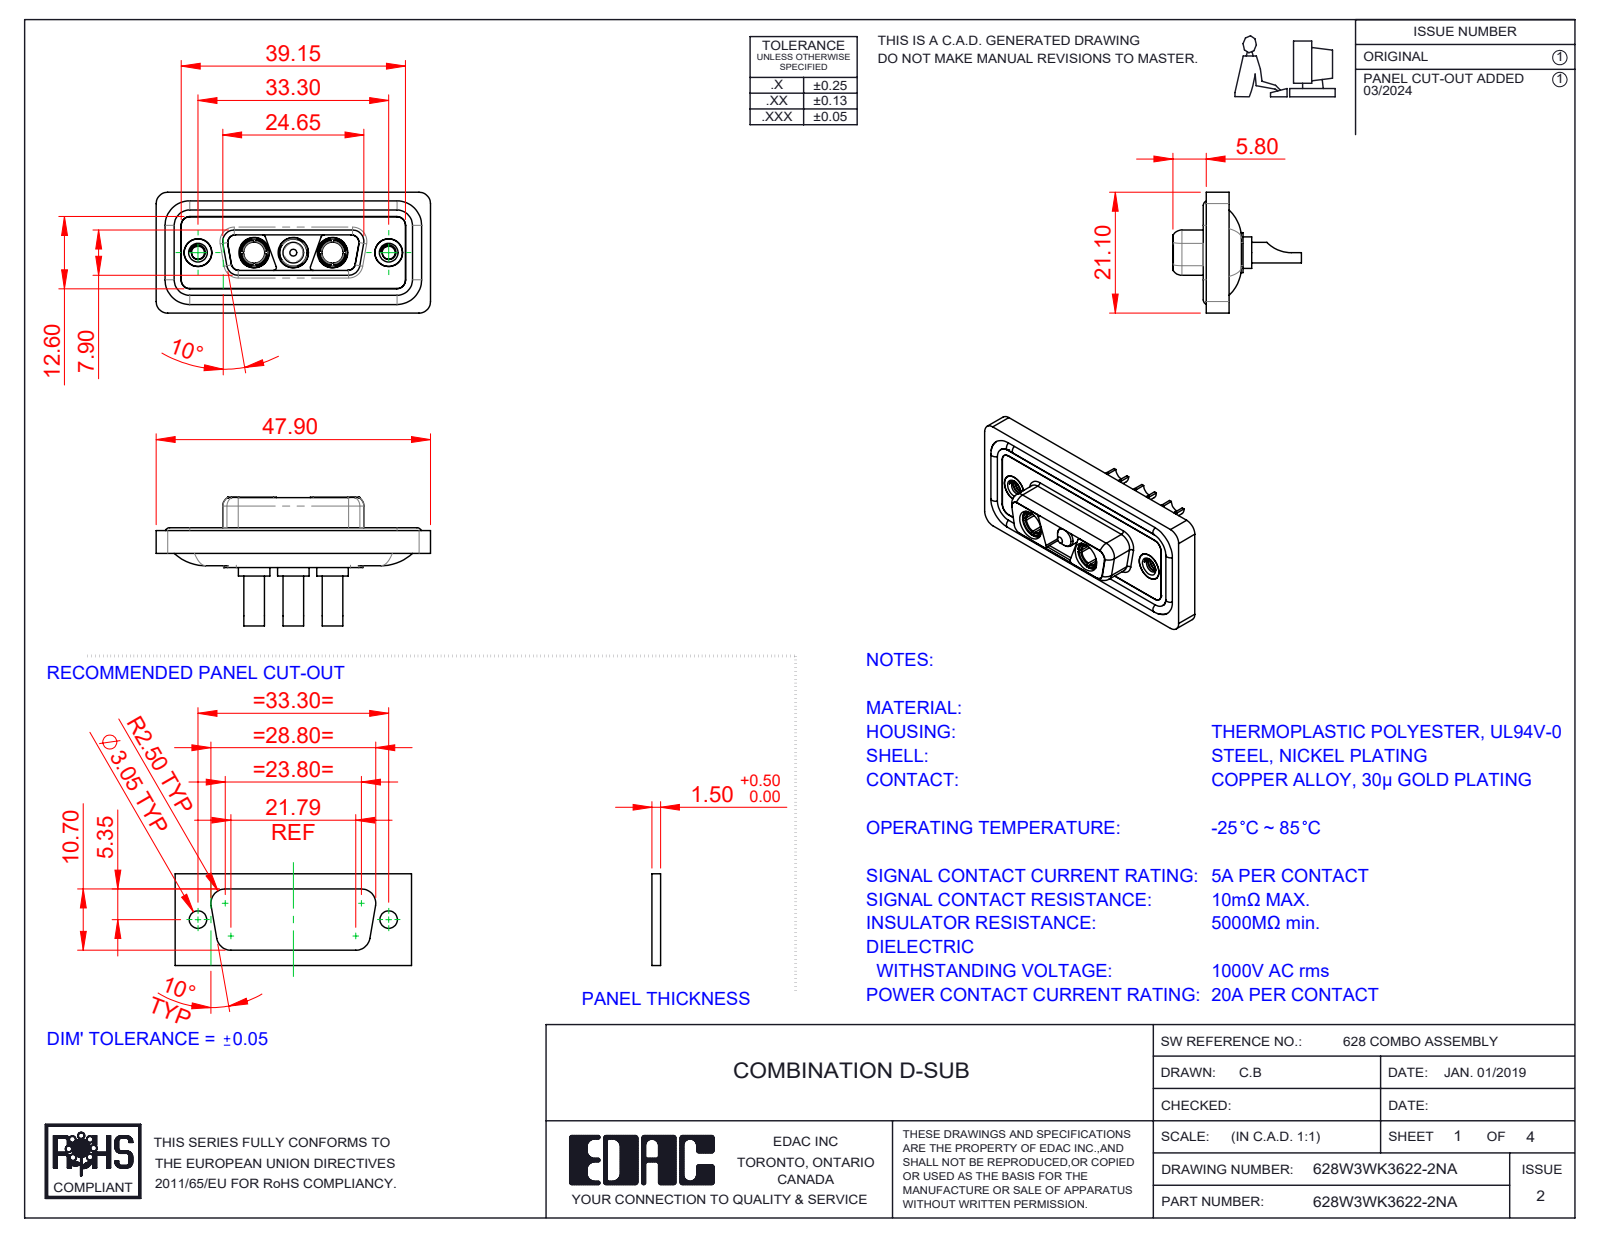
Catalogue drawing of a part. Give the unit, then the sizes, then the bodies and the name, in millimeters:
Units: millimetres
Overall size (bounding box): 47.9 × 22.45 × 21.1
Round holes (diameter × count): ⌀4.85 ×5, ⌀2.7 ×3, ⌀5.3 ×3, ⌀2.26 ×2, ⌀3.7 ×2, ⌀4 ×2, ⌀4.05 ×2, ⌀5 ×2
Round bosses / shafts (diameter × count): ⌀1.6 ×4, ⌀5.5 ×3, ⌀5.2 ×3, ⌀4.75 ×3, ⌀3.75 ×3, ⌀3.6 ×3, ⌀4.96 ×2, ⌀4.95 ×2
Partial cylindrical surfaces — rounded edges, fillets, slot ends (radius × count): R1.5 ×22, R2 ×20, R1.35 ×12, R0.5 ×8, R1.6 ×8, R0.25 ×4, R0.6 ×4, R0.65 ×4
Main face-to-face distances: 0.4, 1.6, 0.5, 1.8, 1.1, 2.9, 5.65, 7.05, 5.35, 1.5
Hole centre spacings: 6.85, 9.8, 16.65, 23.5, 13.7, 33.3
Volume: 5 918 mm³ · Surface area: 9 750 mm²
Bodies: 13 solids, 600 faces (187 planar, 269 cylindrical, 144 other)
Part name (STEP PRODUCT): 628Combo Waterproof Housing_15 Contacts; 628Combo Shell Front_15 Contacts; 628Combo Housing_3WK3; Power Pin_20A SC (+4 more)
STEP written by: SolidWorks 2023 (CONFIG_CONTROL_DESIGN)
